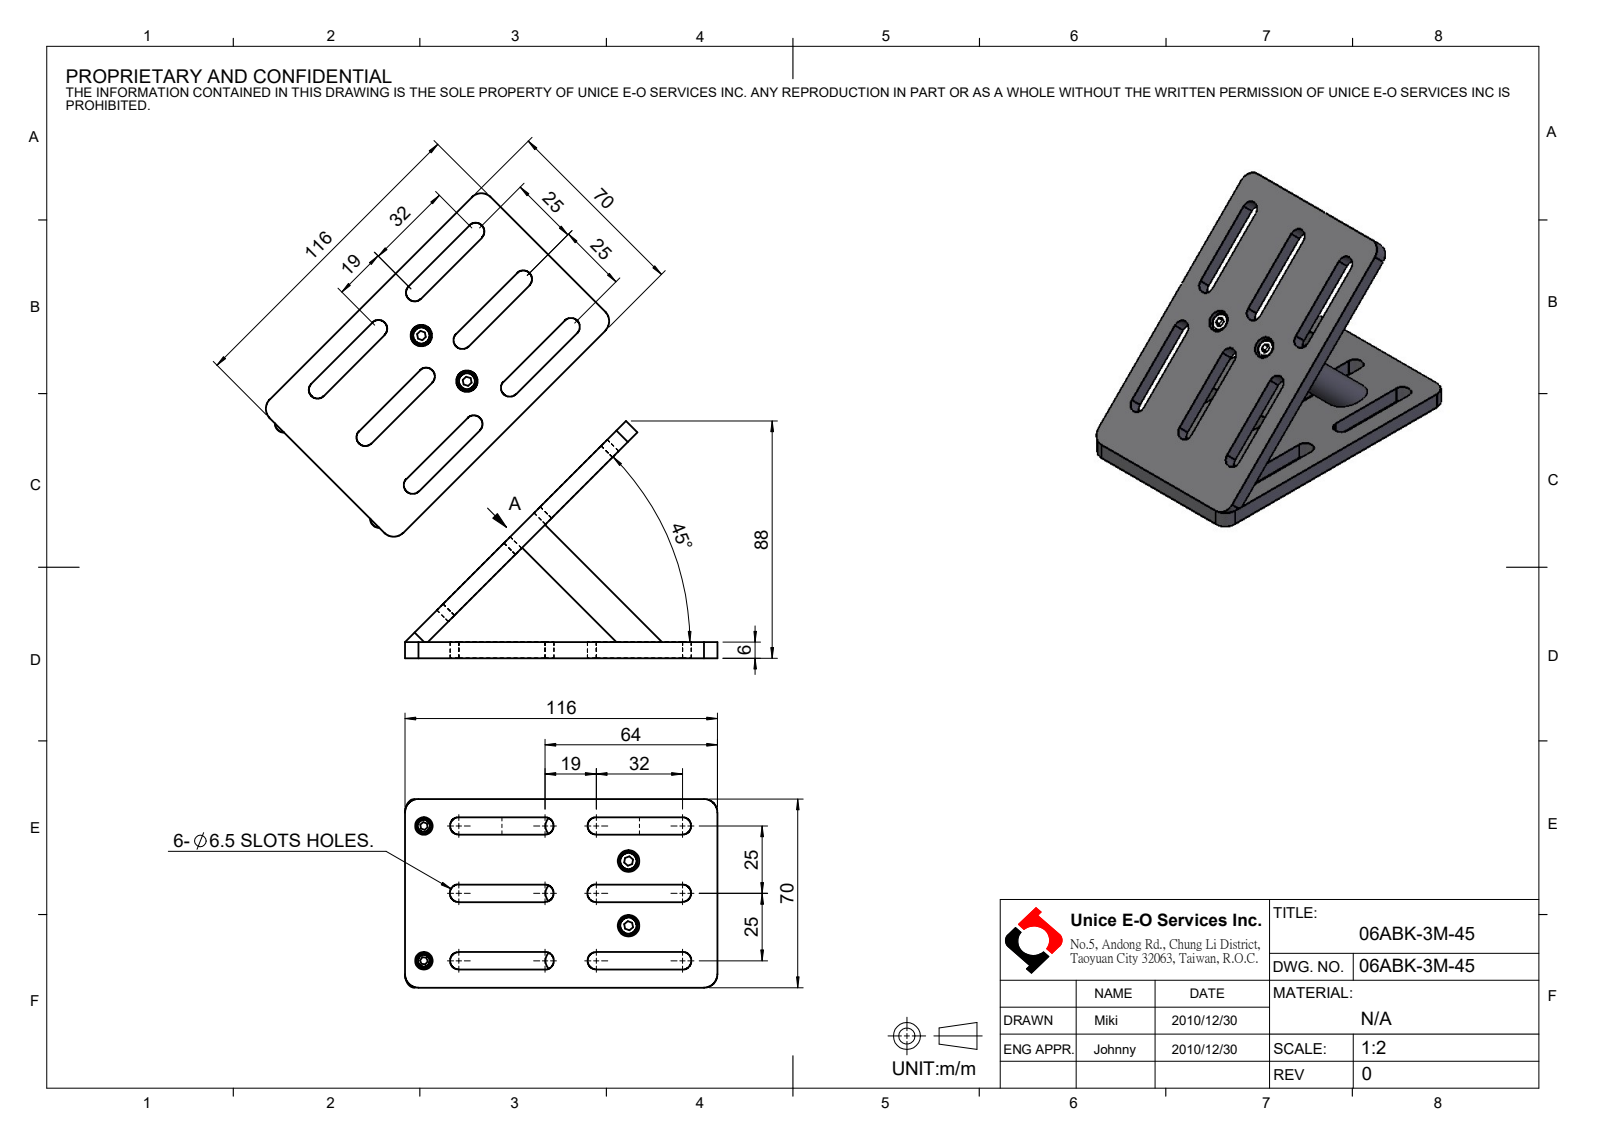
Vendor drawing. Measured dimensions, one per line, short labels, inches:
name: 06ABK-3M-45
written by: SolidWorks 2016 (CONFIG_CONTROL_DESIGN)
unit: in
bodies: 10 solids, 244 faces (106 planar, 102 cylindrical, 36 other)
size: 4.567 × 3.465 × 2.756
volume: 5.522 in³; area: 68.09 in²
holes: 4× ⌀0.13, 4× ⌀0.177, 4× ⌀0.315, 2× ⌀0.098, 2× ⌀0.134, 2× ⌀0.256
bosses: 4× ⌀0.276, 4× ⌀0.157, 2× ⌀0.472, 2× ⌀0.217, 2× ⌀0.118
rounds: 24× R0.128, 8× R0.197
face distances: 0.236, 0.984, 0.256, 1.25, 1.506, 0.522, 2.234, 0.266, 2.49, 0.728
hole spacings: 0.945, 3.035, 3.328, 1.969
